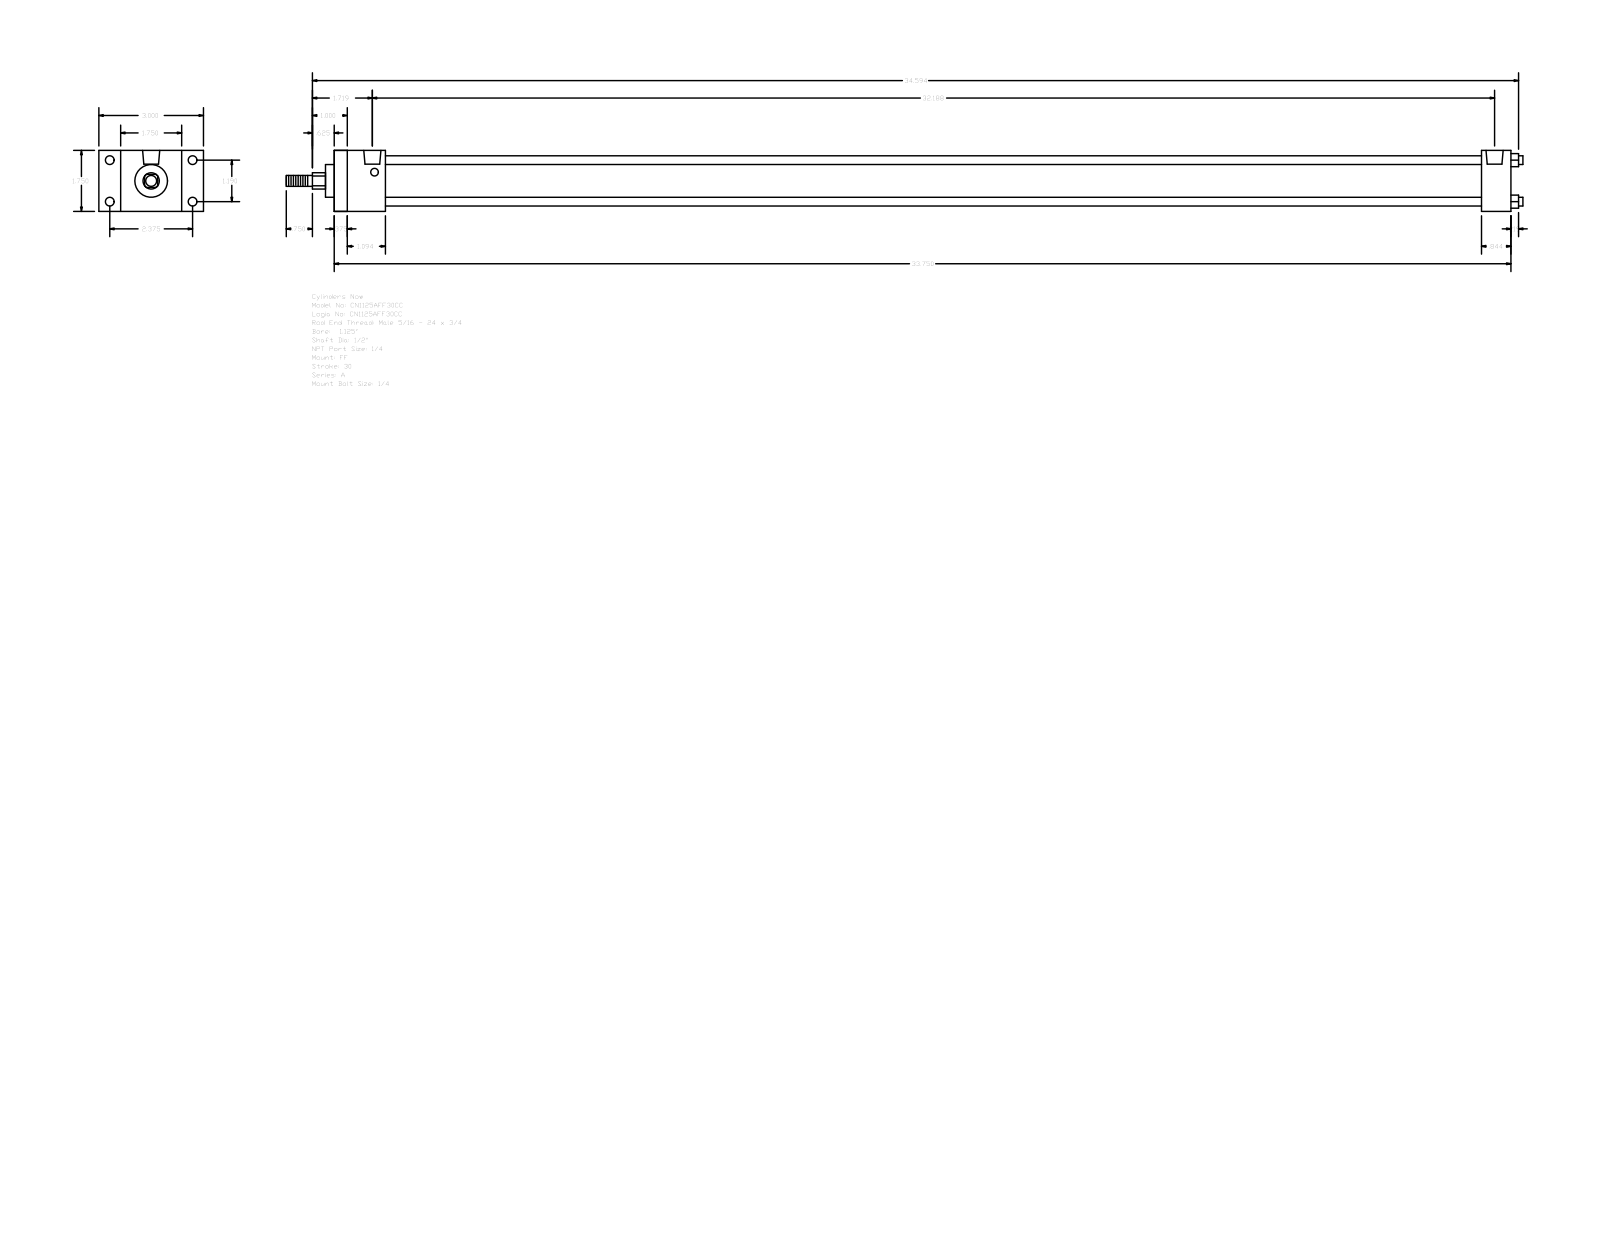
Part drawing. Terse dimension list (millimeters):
name: A_FF__0112_0.5
written by: GSSL Pune (CONFIG_CONTROL_DESIGN)
unit: mm
bodies: 0 solids, 92 faces (64 planar, 28 cylindrical, 0 other)
size: 900.91 × 76.2 × 44.45
holes: 4× ⌀5.56, 4× ⌀6.35, 2× ⌀12.49
bosses: 4× ⌀6.35, 1× ⌀31.88, 1× ⌀23.81, 1× ⌀12.7, 1× ⌀7.94
rounds: 1× R5.94
face distances: 44.46, 857.24, 9.52, 847.72, 15.87, 835.81, 826.29, 21.43, 37.3, 27.78
hole spacings: 30.22, 60.32, 67.47, 814.39, 1.58, 1.59, 815.97, 815.98
